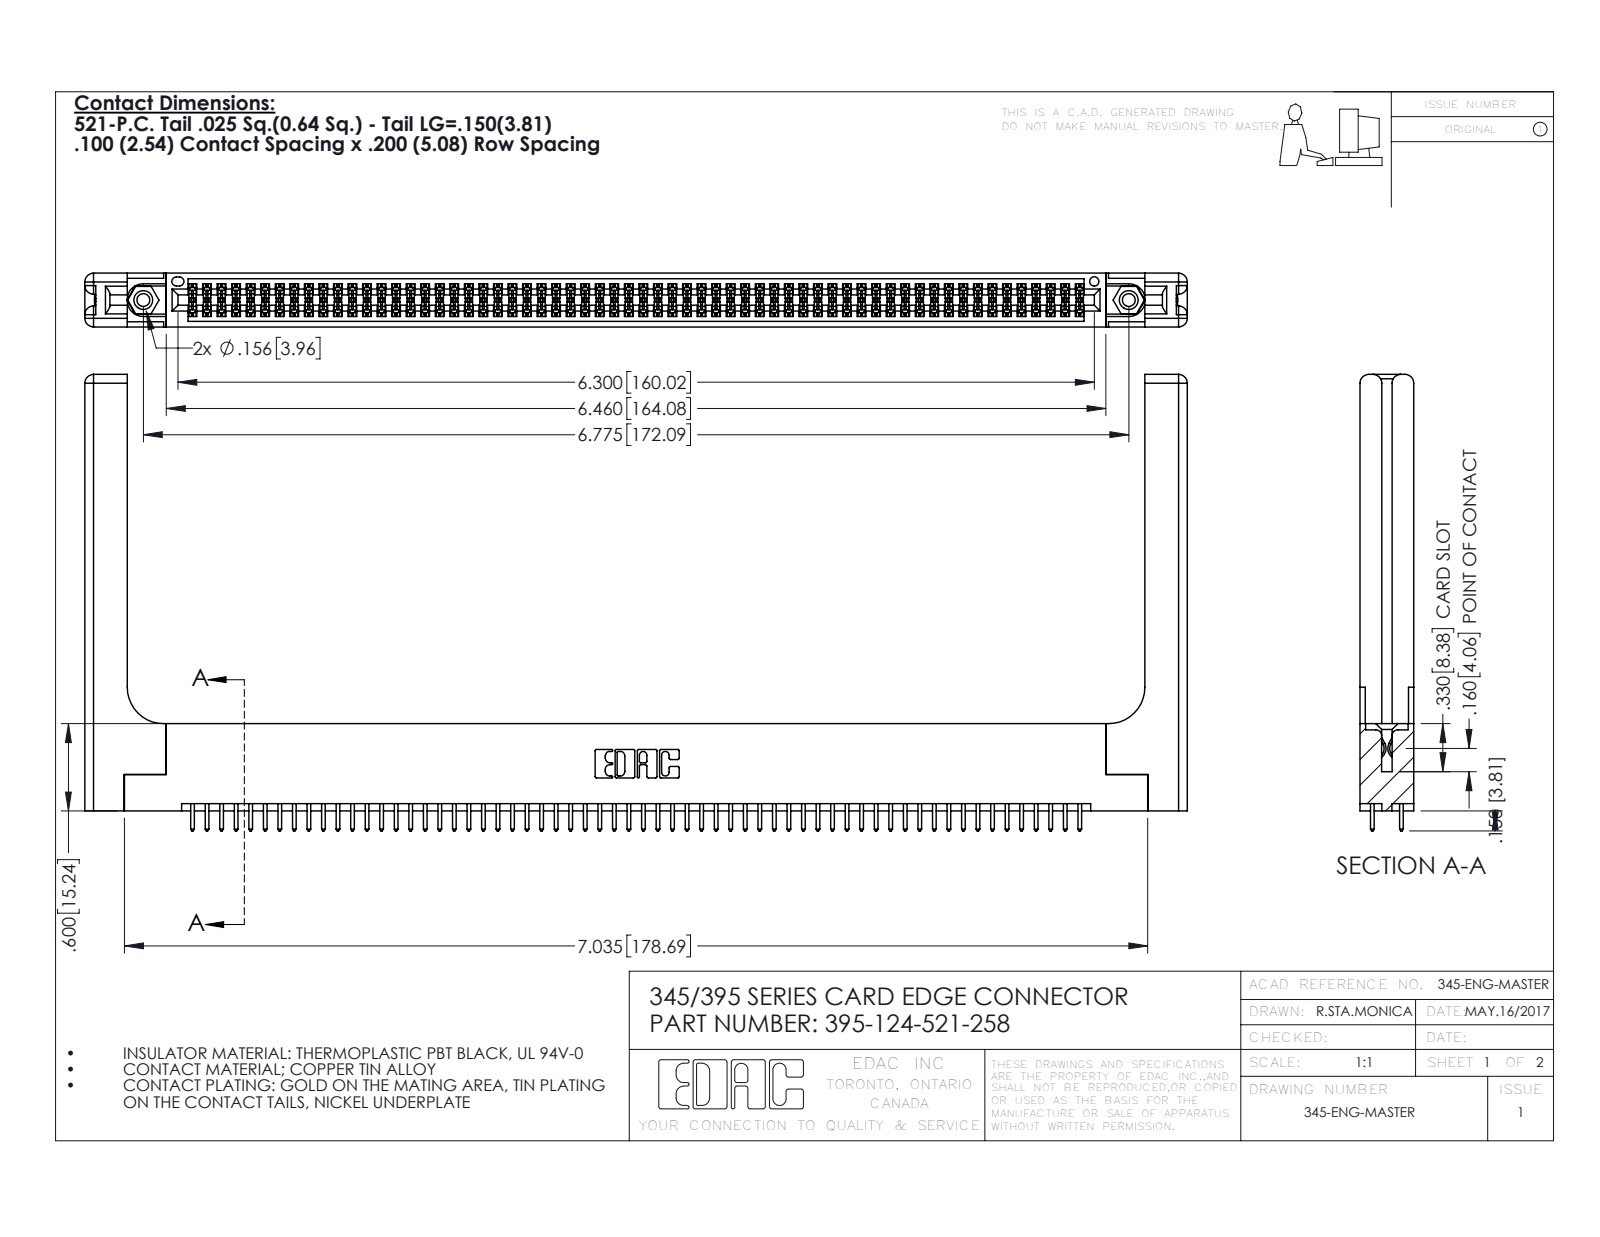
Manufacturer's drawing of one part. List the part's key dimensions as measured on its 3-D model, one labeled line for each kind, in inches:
Part name (STEP PRODUCT): 395-124-521-258; 345-220-058_345-220-058; 345-250-001_345-250-001-102; 345 Part_Flush Mounting Lugs - 0.156 Dia-TH (+1 more)
STEP written by: SolidWorks 2016 (CONFIG_CONTROL_DESIGN)
Units: inches
Bodies: 129 solids, 6582 faces (4320 planar, 2202 cylindrical, 60 other)
Overall size (bounding box): 7.579 × 3.137 × 0.37
Volume: 1.667 in³ · Surface area: 51.09 in²
Round holes (diameter × count): ⌀0.089 ×2, ⌀0.125 ×2, ⌀0.156 ×2, ⌀0.064 ×1
Round bosses / shafts (diameter × count): ⌀0.155 ×2
Partial cylindrical surfaces — rounded edges, fillets, slot ends (radius × count): R0.006 ×186, R0.01 ×124, R0.01 ×22, R0.06 ×16, R0.007 ×6, R0.031 ×6, R0.026 ×3, R0.014 ×2
Main face-to-face distances: 0.072, 0.298, 0.37, 0.2, 0.098, 0.272, 0.025, 0.225, 0.175, 0.15
Hole centre spacings: 0.27, 6.539, 6.775
